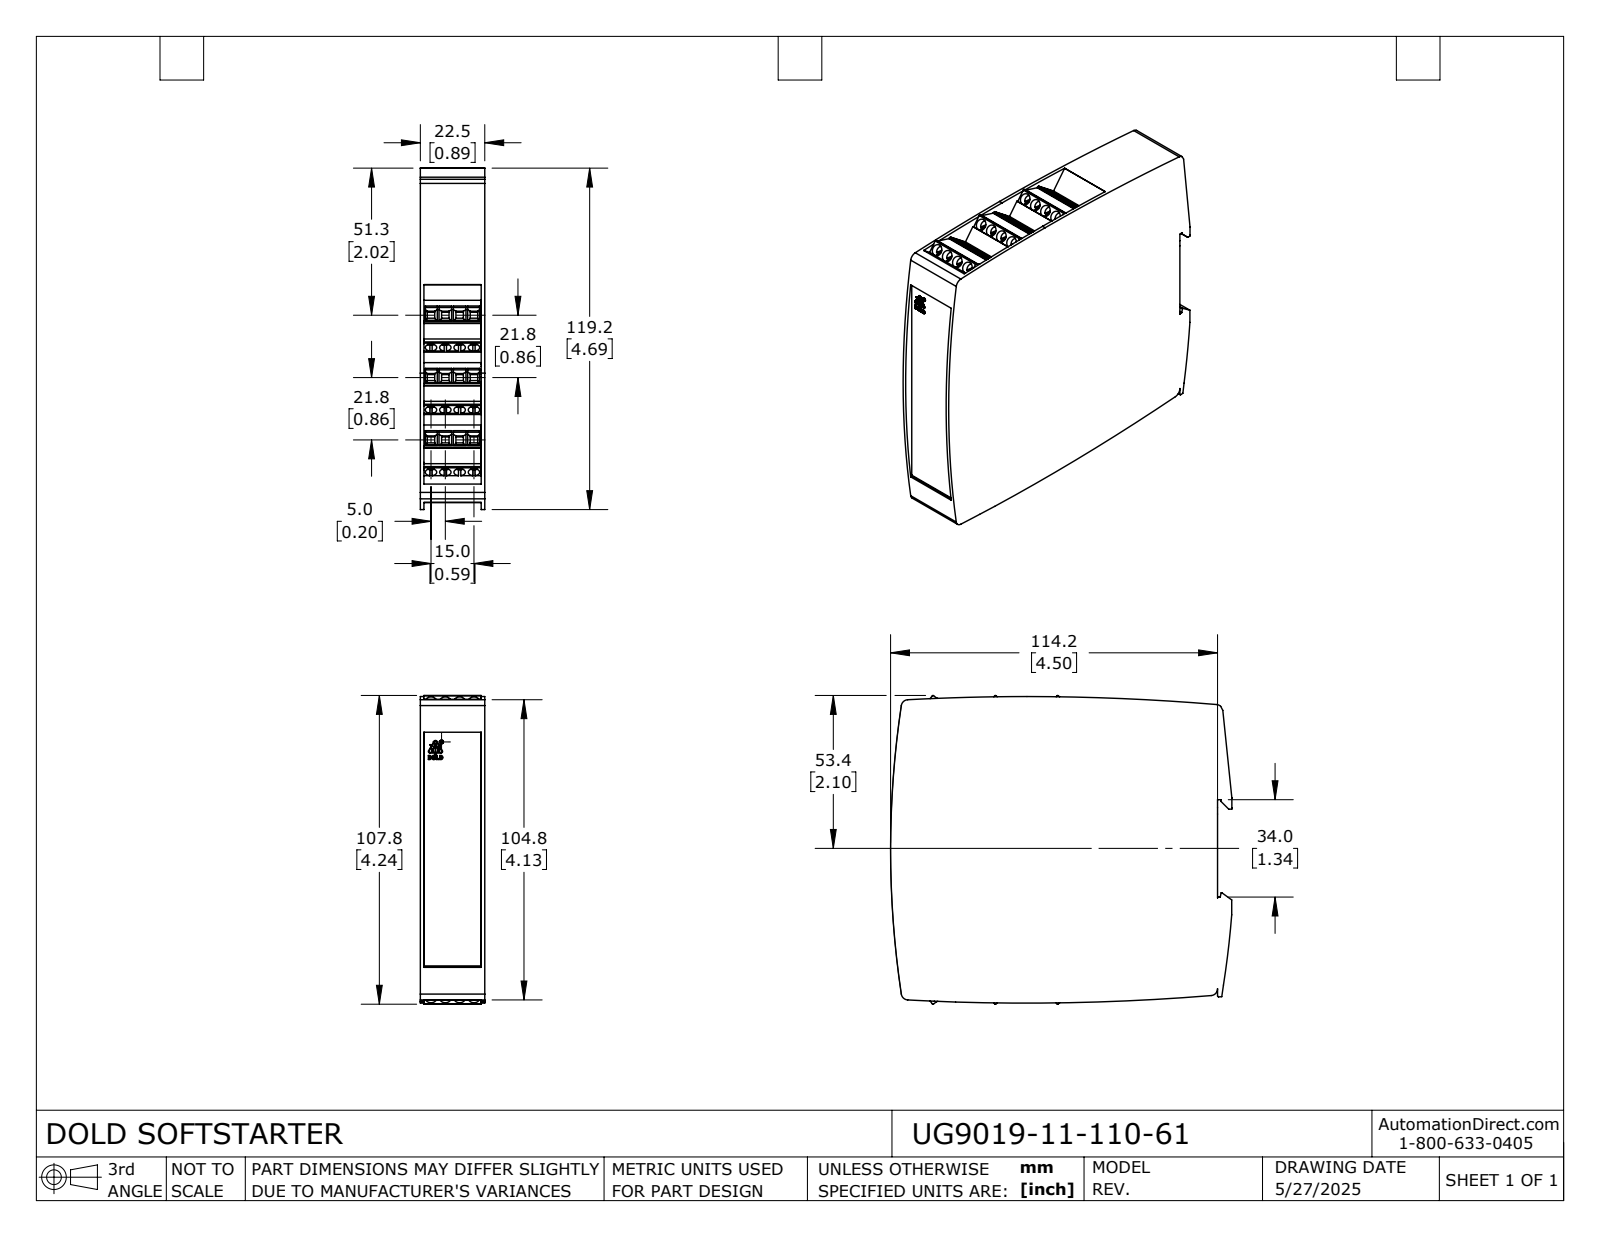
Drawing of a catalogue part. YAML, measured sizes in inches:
part_name: "UG9019-11-110-61"
step_written_by: "SolidWorks 2024 (AUTOMOTIVE_DESIGN)"
units: inches
bodies: {solids: 1, faces: 1036, planar: 813, cylindrical: 222, other: 1}
overall_size: [4.693, 4.243, 0.886]
volume: 15.85
surface_area: 64.72
round_holes:
  - {diameter: 0.157, count: 24}
  - {diameter: 0.053, count: 1}
round_bosses_or_shafts:
  - {diameter: 0.15, count: 24}
  - {diameter: 0.049, count: 1}
partial_cylinders:
  - {radius: 0.012, count: 15}
  - {radius: 0.02, count: 14}
  - {radius: 0.004, count: 12}
  - {radius: 0.094, count: 7}
  - {radius: 0.005, count: 6}
  - {radius: 0.004, count: 4}
  - {radius: 31.496, count: 4}
  - {radius: 0.021, count: 3}
face_to_face_distances: [0.886, 0.049, 0.837, 0.675, 4.379, 0.051, 0.835, 1.35, 0.528, 0.785]
hole_center_spacings: [0.563, 0.197, 0.528, 0.658, 0.394, 1.073, 0.792, 1.055]
